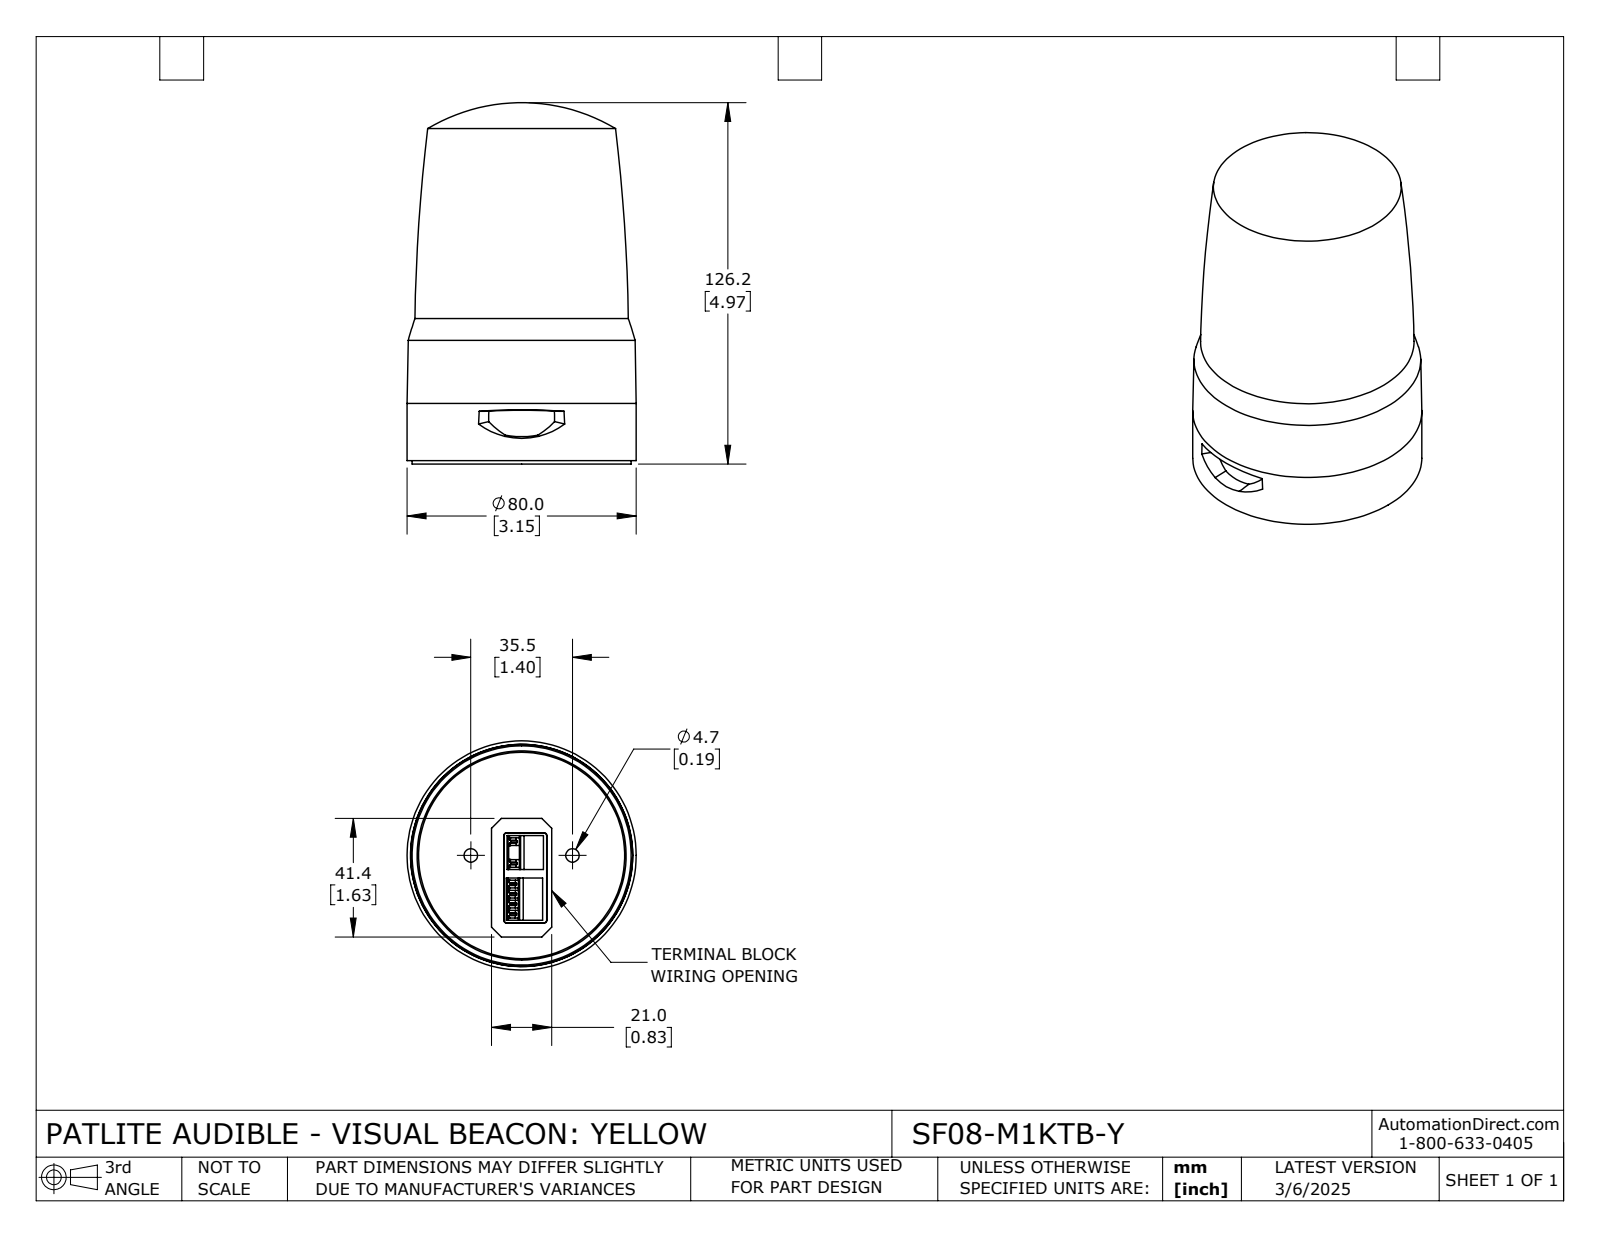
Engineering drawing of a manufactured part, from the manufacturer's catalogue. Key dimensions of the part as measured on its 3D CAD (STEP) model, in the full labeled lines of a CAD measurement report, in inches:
Part name (STEP PRODUCT): SF08-M1KTB-Y
STEP written by: SolidWorks 2024 (CONFIG_CONTROL_DESIGN)
Units: inches
Bodies: 2 solids, 262 faces (168 planar, 32 cylindrical, 62 other)
Overall size (bounding box): 4.969 × 3.15 × 3.15
Volume: 29.79 in³ · Surface area: 84.61 in²
Round holes (diameter × count): ⌀0.185 ×2, ⌀0.48 ×2, ⌀2.874 ×1
Round bosses / shafts (diameter × count): ⌀3.15 ×1, ⌀3.012 ×1, ⌀2.937 ×1, ⌀2.835 ×1
Partial cylindrical surfaces — rounded edges, fillets, slot ends (radius × count): R0.039 ×4, R0.012 ×2, R1.362 ×1, R1.378 ×1
Main face-to-face distances: 0.618, 0.248, 0.37, 0.118, 0.201, 0.571, 0.124, 0.242, 0.051, 0.49
Hole centre spacings: 0.699, 1.398
